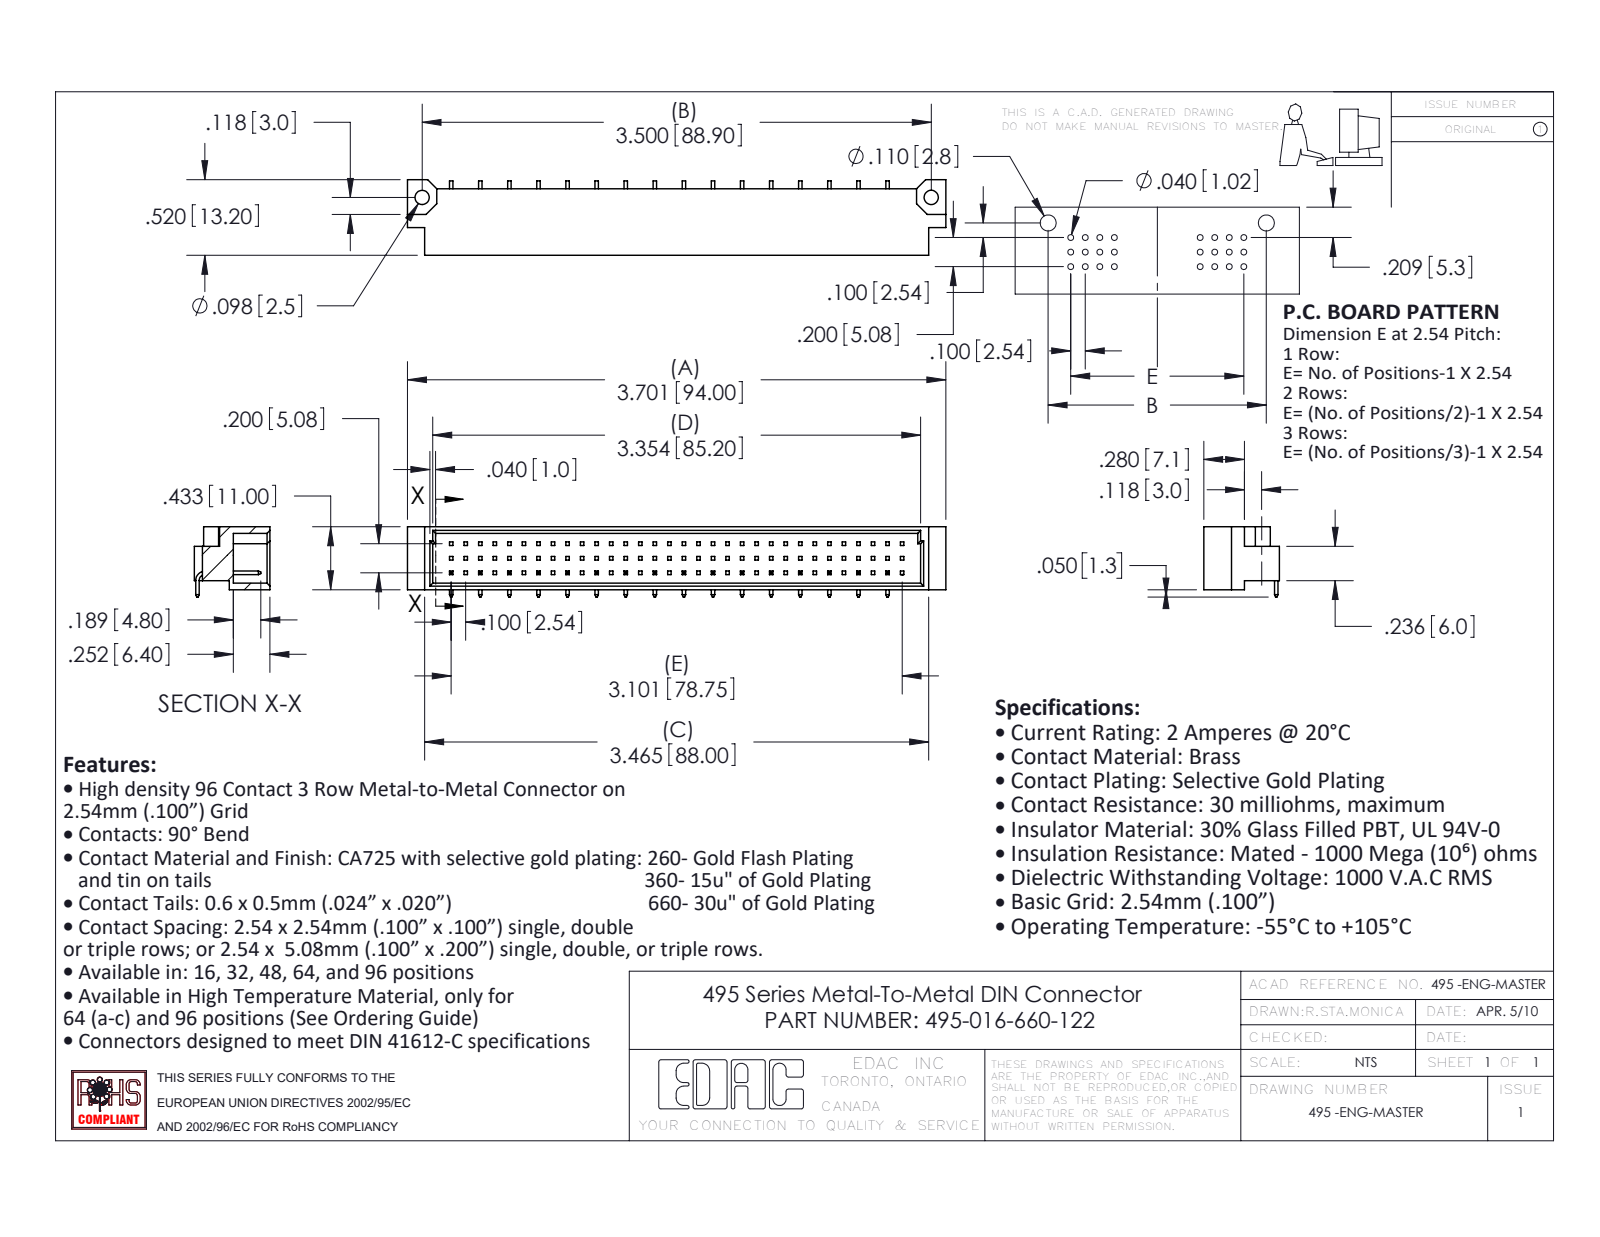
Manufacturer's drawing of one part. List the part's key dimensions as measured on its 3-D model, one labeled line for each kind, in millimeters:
Part name (STEP PRODUCT): 495-016-660-122; 495 Part_96; 495-290-3
STEP written by: SolidWorks 2020 (AUTOMOTIVE_DESIGN)
Units: millimetres
Bodies: 17 solids, 721 faces (685 planar, 36 cylindrical, 0 other)
Overall size (bounding box): 94 × 13.2 × 12.27
Volume: 6 015 mm³ · Surface area: 7 413 mm²
Round holes (diameter × count): ⌀2.49 ×2
Partial cylindrical surfaces — rounded edges, fillets, slot ends (radius × count): R1.02 ×1, R1.65 ×1
Main face-to-face distances: 1.14, 9.86, 5.2, 11, 8.72, 1.6, 9.4, 0.46, 8.26, 0.61
Hole centre spacings: 88.9
